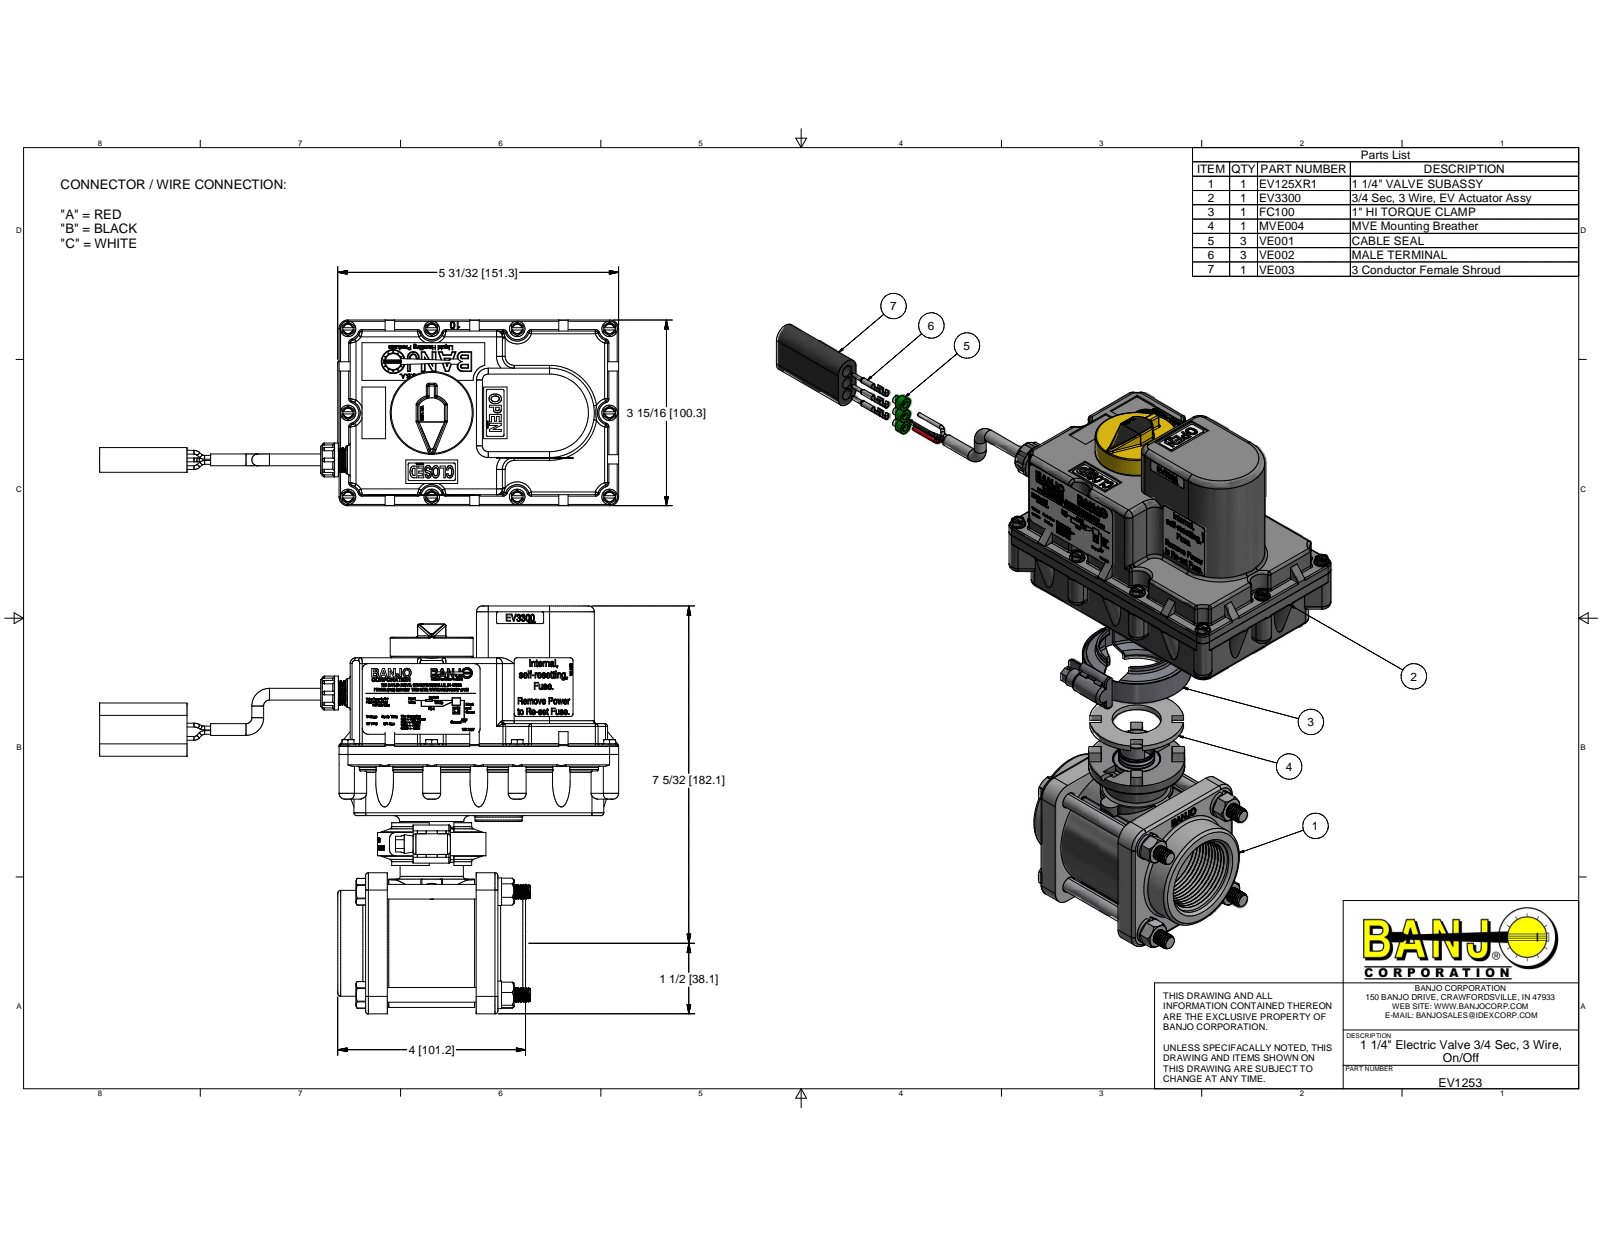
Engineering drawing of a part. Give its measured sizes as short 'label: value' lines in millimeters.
name: MEV10254AX; MEV10254A; VE10155SSH; MEV10151SS (+8 more)
written by: Autodesk Inventor 2016 (AUTOMOTIVE_DESIGN)
unit: mm
bodies: 79 solids, 12776 faces (6232 planar, 1785 cylindrical, 4759 other)
size: 279.69 × 220.16 × 100.33
volume: 880 412 mm³; area: 404 151 mm²
holes: 10× ⌀2.79, 10× ⌀4.06, 10× ⌀5.08, 9× ⌀3.81, 8× ⌀1.32, 8× ⌀2.01, 6× ⌀1.19, 6× ⌀3.05, 6× ⌀4.47, 5× ⌀6.35, 4× ⌀0.38, 4× ⌀6.41
bosses: 60× ⌀6.82, 12× ⌀2.03, 10× ⌀8.33, 10× ⌀3.51, 8× ⌀2.62, 6× ⌀6.35, 5× ⌀1.9, 4× ⌀14.81
rounds: 143× R0.76, 79× R1.52, 62× R0.51, 43× R0.89, 32× R3.17, 24× R8, 24× R12.7, 16× R9.91
face distances: 3.17, 3.18, 27.94, 5.08, 26.04, 19.81, 33.02, 82.04, 20.07, 76.96
hole spacings: 42.68, 52.27, 42.78, 45.34, 60.36, 2.77, 12.5, 30.18
